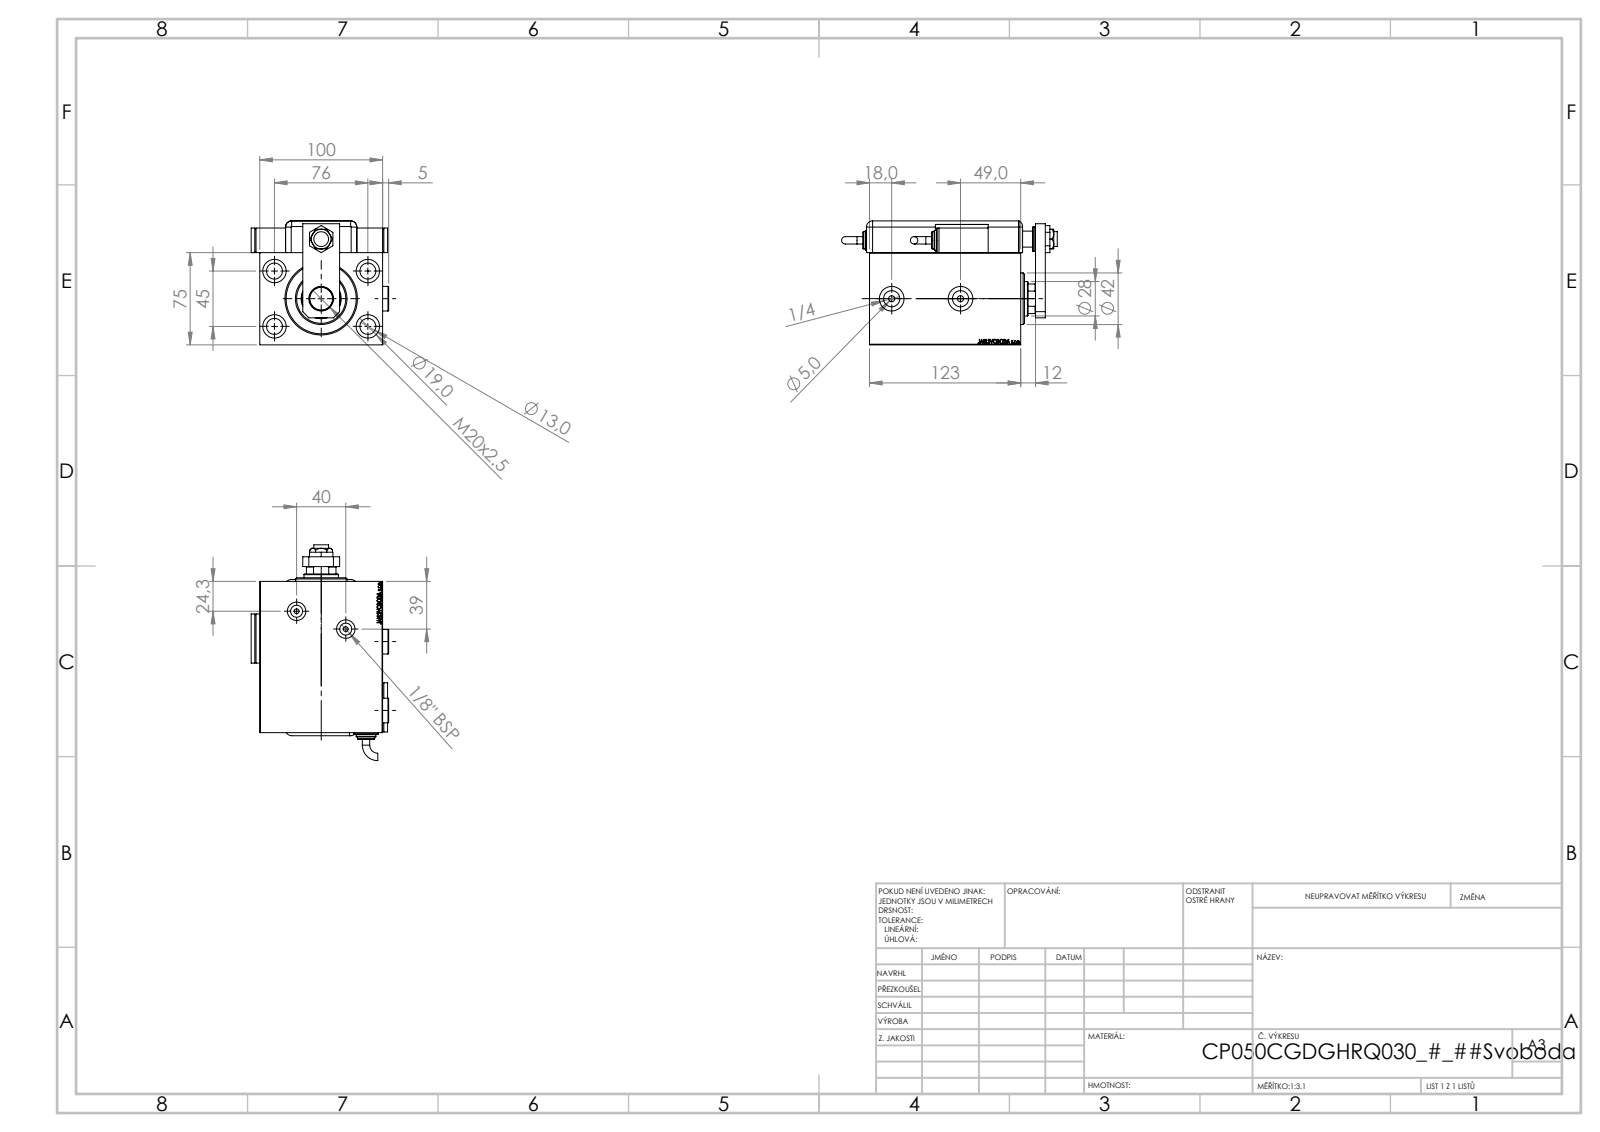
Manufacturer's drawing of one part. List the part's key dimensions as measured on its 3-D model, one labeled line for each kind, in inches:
Part name (STEP PRODUCT): NUT_D19; TYC; V450CP_C; PLUG (+7 more)
STEP written by: SolidWorks 2019 (CONFIG_CONTROL_DESIGN)
Units: inches
Bodies: 15 solids, 1327 faces (655 planar, 147 cylindrical, 525 other)
Overall size (bounding box): 6.908 × 4.406 × 3.969
Volume: 57.91 in³ · Surface area: 305.6 in²
Round holes (diameter × count): ⌀0.512 ×5, ⌀0.157 ×4, ⌀0.748 ×4, ⌀0.787 ×3, ⌀0.197 ×2, ⌀0.315 ×2, ⌀0.383 ×2, ⌀0.518 ×2, ⌀0.591 ×2, ⌀0.472 ×1, ⌀0.551 ×1, ⌀0.728 ×1
Round bosses / shafts (diameter × count): ⌀0.787 ×3, ⌀0.63 ×2, ⌀0.551 ×2, ⌀0.236 ×2, ⌀1.654 ×1
Partial cylindrical surfaces — rounded edges, fillets, slot ends (radius × count): R0.197 ×9, R0.394 ×1, R0.531 ×1
Main face-to-face distances: 2.953, 0.118, 3.937, 1.016, 3.969, 0.551, 0.787, 4.843, 4.291, 3.11
Hole centre spacings: 1.739, 1.772, 1.813, 2.992, 3.17, 3.477, 0.72, 0.787
